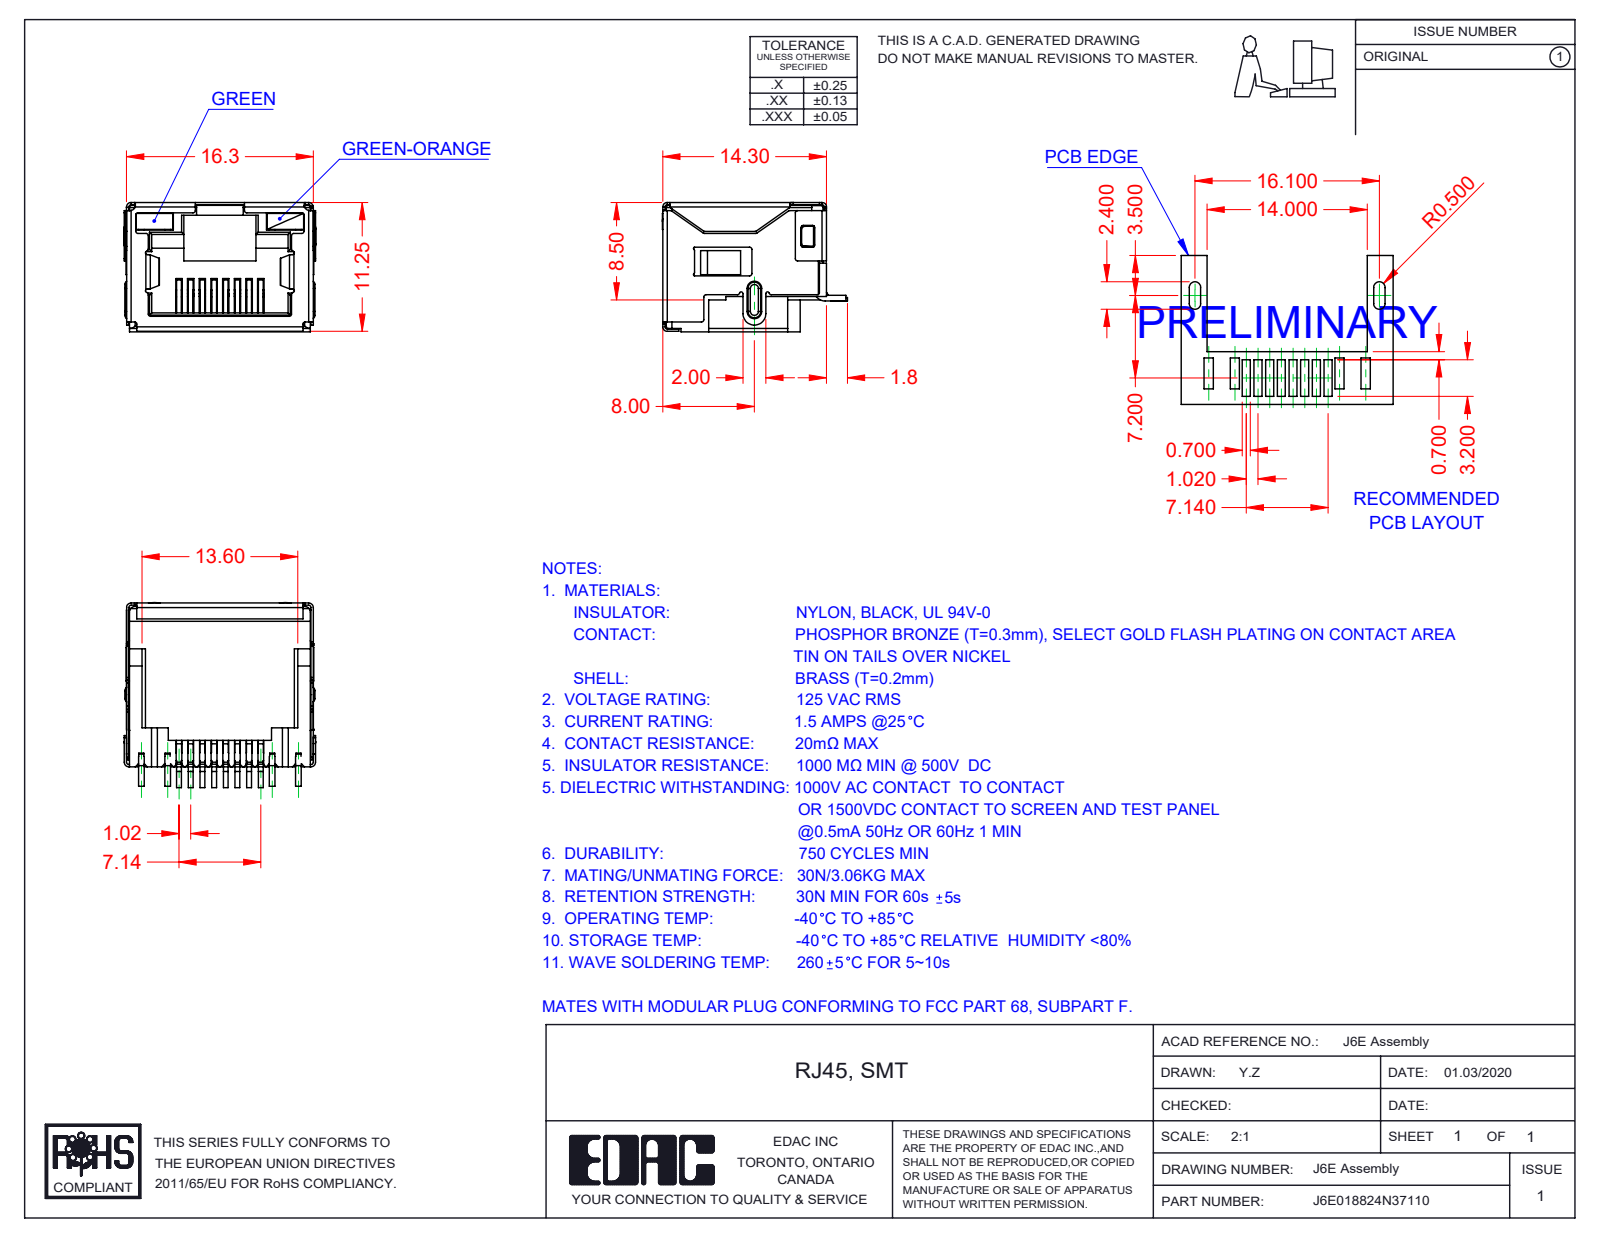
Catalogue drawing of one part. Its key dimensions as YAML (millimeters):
part_name: "6E Contacts; 6E LED LH_3-Green; J6E018824N37110; 6E Shield_LED (+2 more)"
step_written_by: "SolidWorks 2016 (CONFIG_CONTROL_DESIGN)"
units: millimeters
bodies: {solids: 12, faces: 1498, planar: 1099, cylindrical: 349, other: 50}
overall_size: [16.75, 16.15, 11.3]
volume: 1109
surface_area: 4045
partial_cylinders:
  - {radius: 0.2, count: 82}
  - {radius: 0.25, count: 17}
  - {radius: 0.4, count: 13}
  - {radius: 0.5, count: 13}
  - {radius: 0.1, count: 10}
  - {radius: 0.15, count: 7}
  - {radius: 0.3, count: 4}
  - {radius: 1, count: 3}
face_to_face_distances: [11.05, 16.05, 16.1, 15.85, 11.1, 11.3, 2.4, 0.7, 9.85, 0.49]
